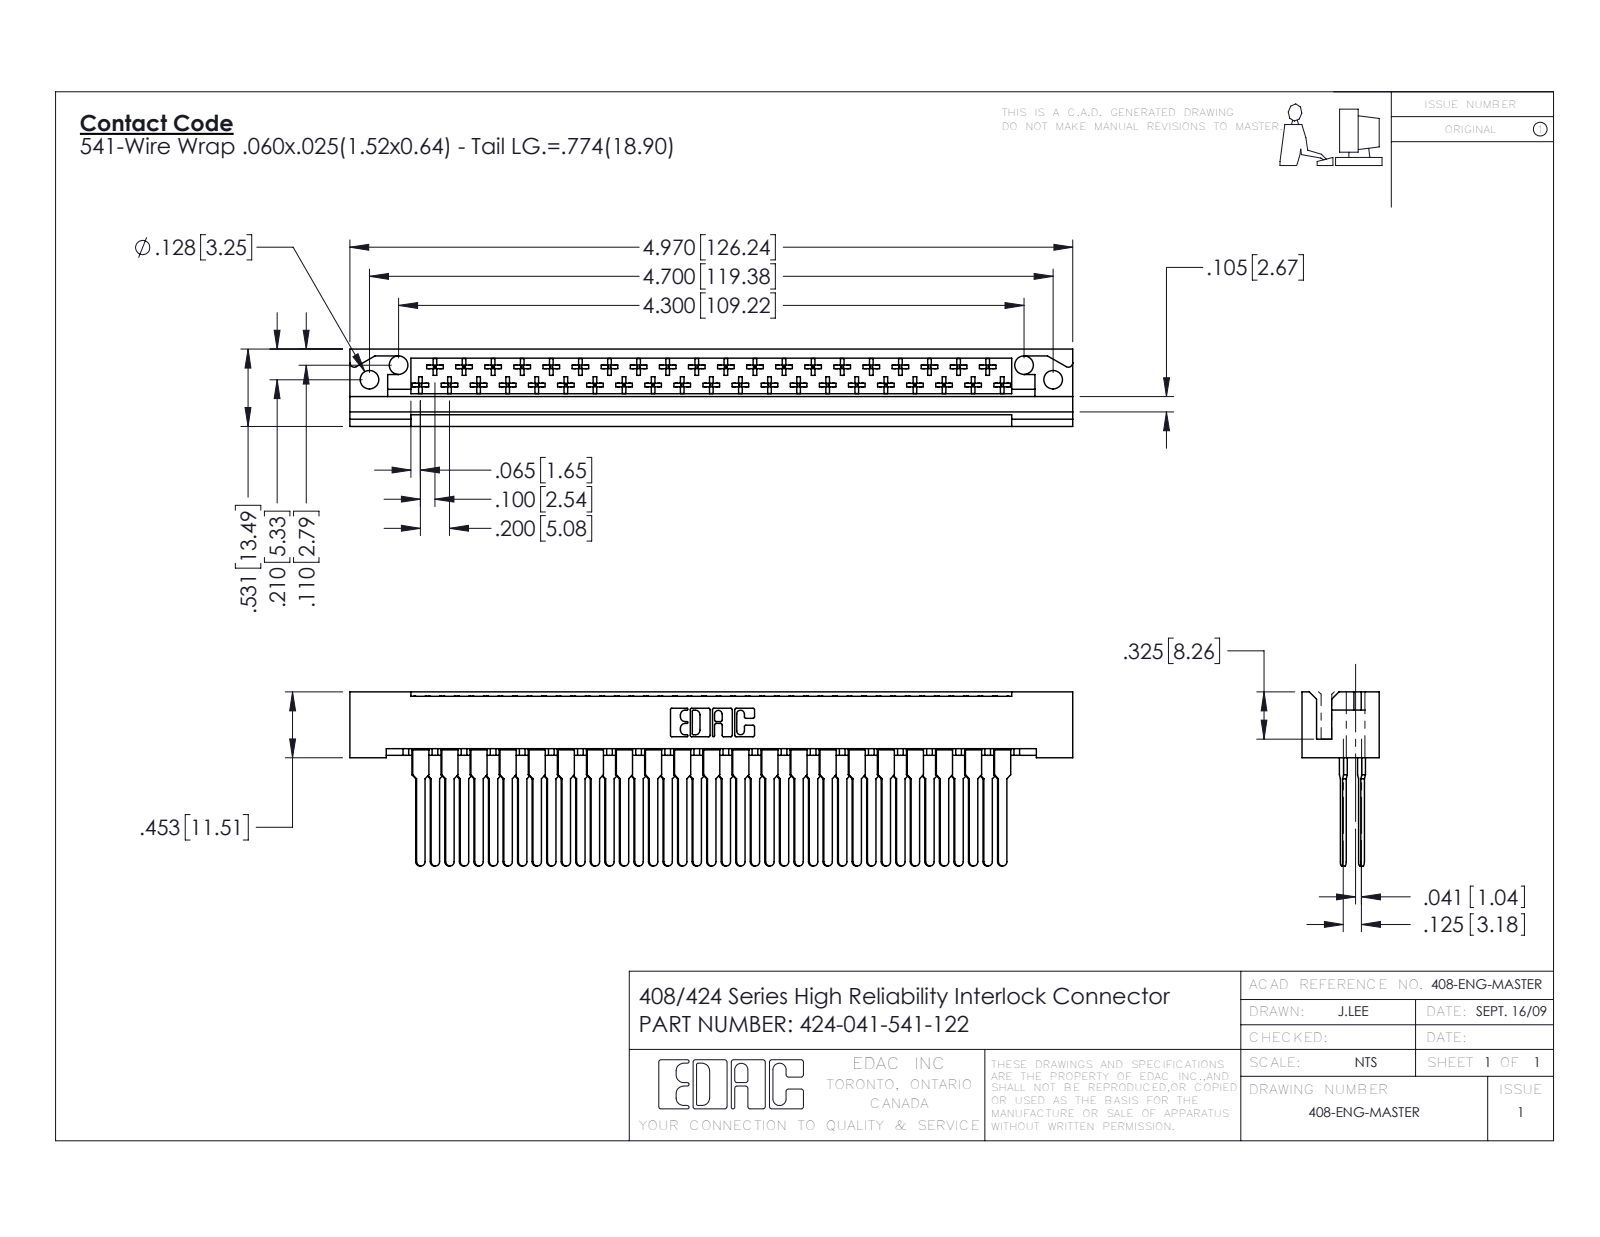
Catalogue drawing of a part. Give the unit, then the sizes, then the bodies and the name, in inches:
Units: inches
Overall size (bounding box): 4.97 × 1.197 × 0.531
Round holes (diameter × count): ⌀0.128 ×4
Partial cylindrical surfaces — rounded edges, fillets, slot ends (radius × count): R0.01 ×246, R0.02 ×43, R0.03 ×43, R0.01 ×22, R0.007 ×6, R0.031 ×6, R0.026 ×3
Main face-to-face distances: 0.1, 0.296, 0.025, 0.531, 0.125, 0.235, 0.259, 0.272, 0.025, 0.217
Hole centre spacings: 0.224, 4.501, 4.3, 4.7
Volume: 0.844 in³ · Surface area: 31.41 in²
Bodies: 42 solids, 2318 faces (1729 planar, 425 cylindrical, 164 other)
Part name (STEP PRODUCT): 424-047-541-122; 408-290-001_408-290-141; 424 Part_041
STEP written by: SolidWorks 2016 (CONFIG_CONTROL_DESIGN)
